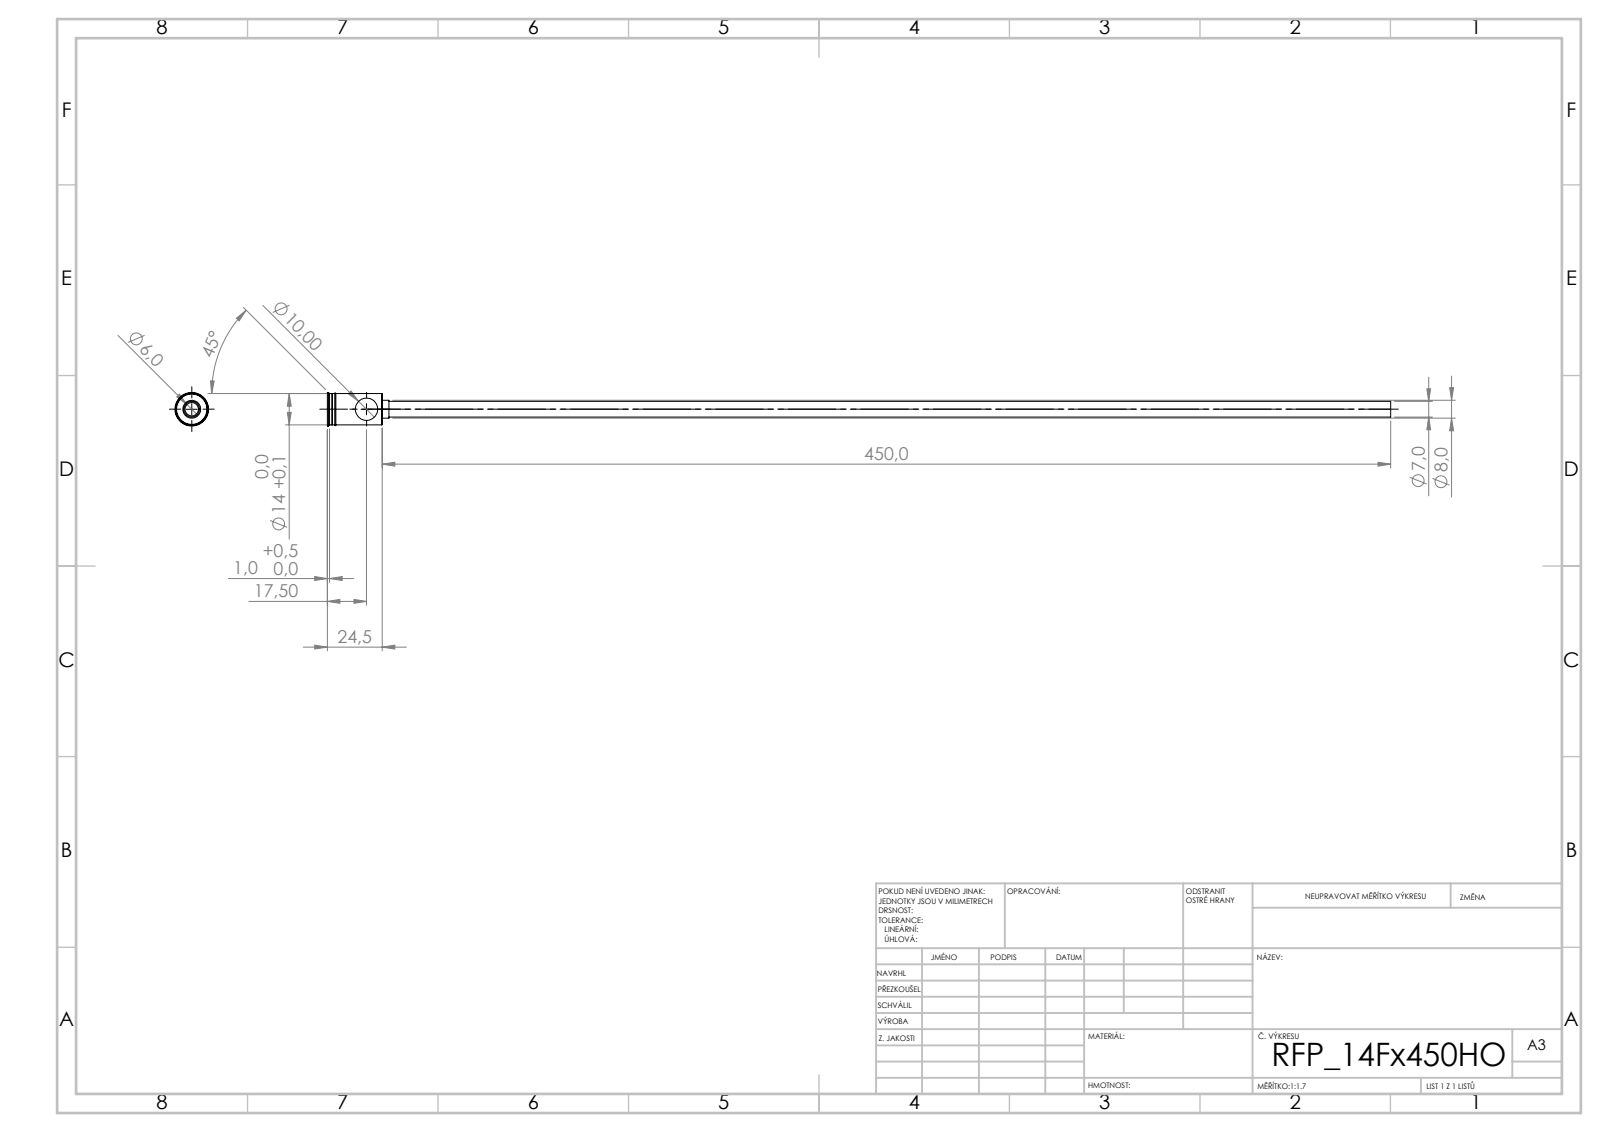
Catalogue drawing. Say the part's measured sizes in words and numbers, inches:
Its 3-D file was written by "SolidWorks 2019 (CONFIG_CONTROL_DESIGN)". It is 1 solid with 44 faces: 20 planar, 16 cylindrical and 8 other. Overall it measures 18.681 by 0.591 by 0.591 inches. Its volume is 0.438 cubic inches and its surface area 31.15 square inches. Round holes: 1 of diameter 0.236, 1 of diameter 0.394. Round bosses or shafts: 1 of diameter 0.591, 1 of diameter 0.551, 1 of diameter 0.315, 1 of diameter 0.276. The main face-to-face distances are 0.965, 0.886, 0.079, 0.37, 0.874, 0.091, 0.118, 0.992, 1.004, 1.083.
